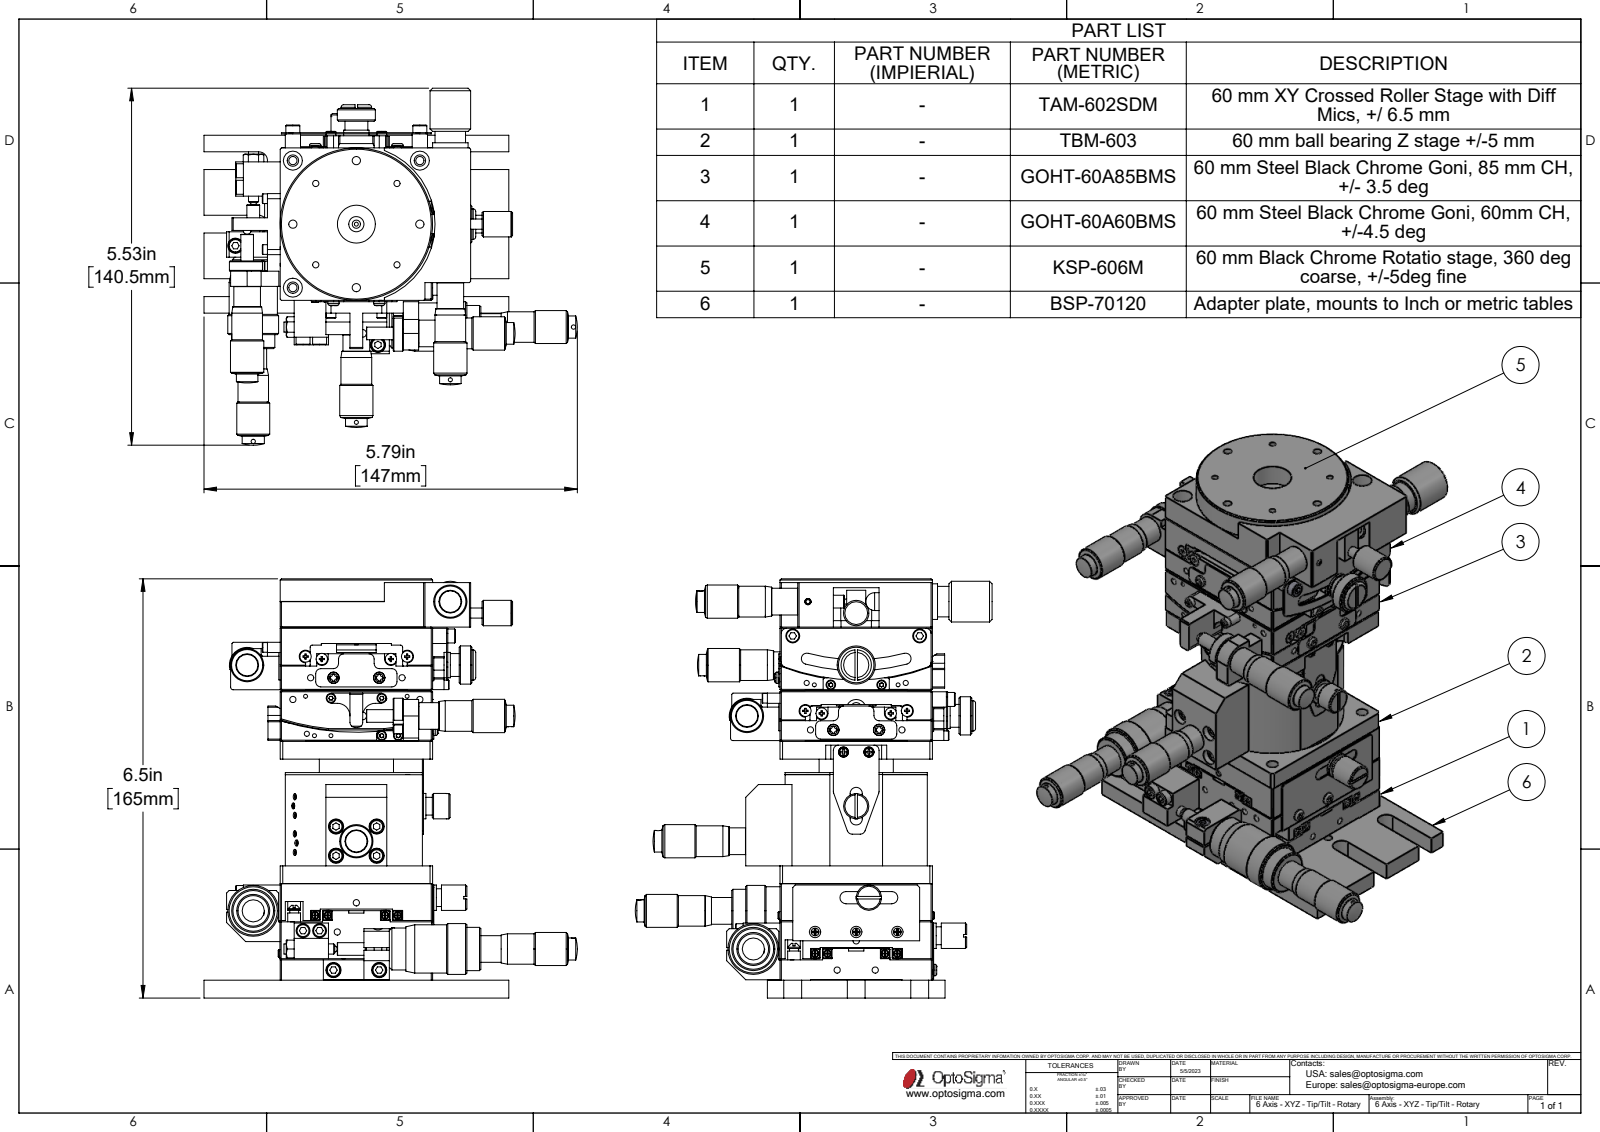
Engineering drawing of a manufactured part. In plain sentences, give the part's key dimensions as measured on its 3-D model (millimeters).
The part is named "KSP-606M(2)^KSP-606M; TBM-603-C1-S09.stp; KSP-60-C1A-S05^KSP-606M(2)_KSP-606M; TBM-603-04.stp (+8 more)". Its 3-D file was written by "SolidWorks 2023 (AUTOMOTIVE_DESIGN)". It is 127 solids with 7570 faces: 3119 planar, 1360 cylindrical and 3091 other. Overall it measures 165 by 147 by 140.5 millimeters. Its volume is 315 402 cubic millimeters and its surface area 262 924 square millimeters. Round holes: 58 of diameter 2, 22 of diameter 3, 12 of diameter 2.46, 8 of diameter 1.5, 8 of diameter 2.5, 7 of diameter 5, 6 of diameter 2.6, 6 of diameter 4, 6 of diameter 8.5, 4 of diameter 1.6, 4 of diameter 4.3, 4 of diameter 4.6. Round bosses or shafts: 54 of diameter 3.8, 24 of diameter 4.5, 23 of diameter 3, 22 of diameter 5.5, 12 of diameter 4, 11 of diameter 7, 10 of diameter 3.5, 7 of diameter 10. Partial cylindrical surfaces (rounded edges, fillets, slot ends): 44 of radius 2, 36 of radius 1, 20 of radius 3, 16 of radius 0.9, 12 of radius 5, 8 of radius 0.8, 8 of radius 2.5, 8 of radius 3.5. The main face-to-face distances are 7, 45, 101, 0.5, 60, 15, 20, 94, 38, 146. The hole center spacings are 20, 10, 11.14, 29.26, 20.59, 34, 4.9, 27.5.
